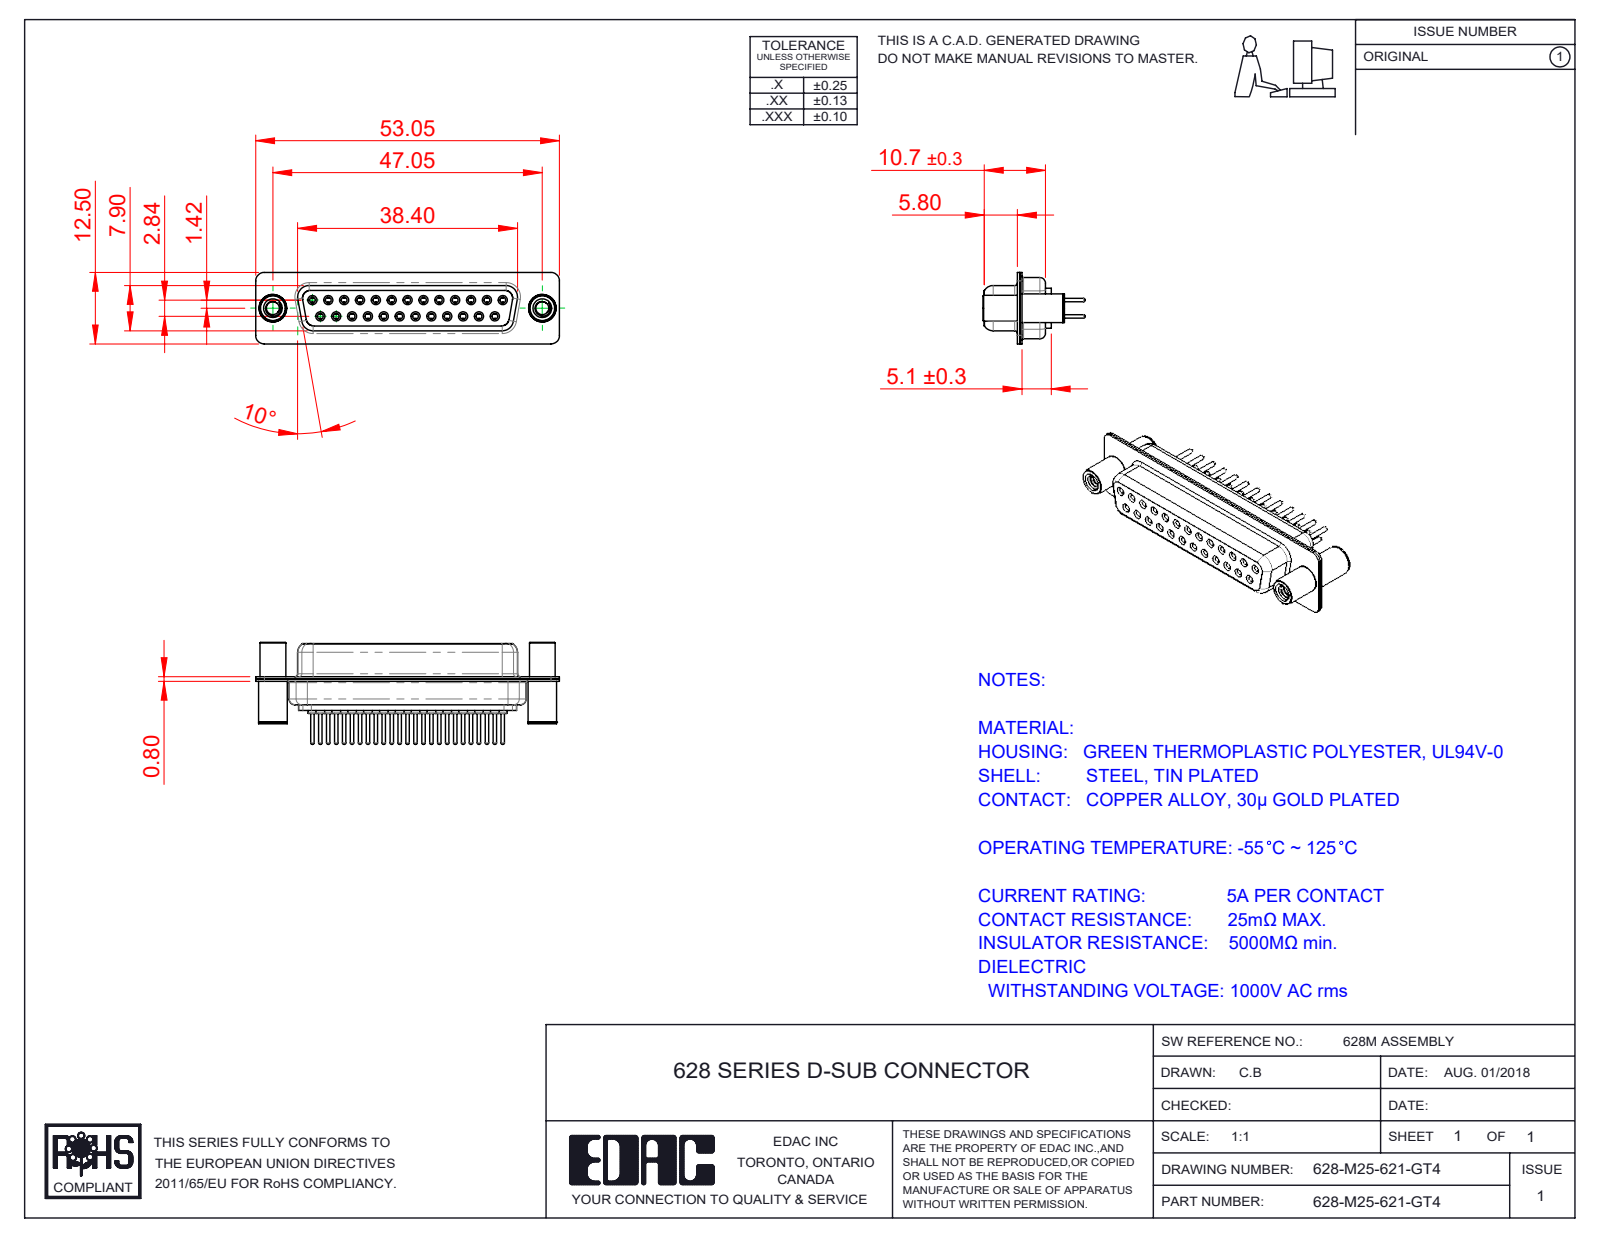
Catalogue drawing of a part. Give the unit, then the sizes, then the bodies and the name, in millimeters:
Units: millimetres
Overall size (bounding box): 53.05 × 17.8 × 12.5
Round holes (diameter × count): ⌀1 ×25, ⌀1.1 ×25, ⌀1.7 ×25, ⌀1.8 ×25, ⌀2 ×25, ⌀2.26 ×2, ⌀3.26 ×2, ⌀4 ×2, ⌀4.8 ×2
Round bosses / shafts (diameter × count): ⌀2.2 ×25, ⌀1.6 ×25, ⌀1.5 ×25, ⌀0.6 ×25, ⌀5 ×2, ⌀4.9 ×2, ⌀4.5 ×2
Partial cylindrical surfaces — rounded edges, fillets, slot ends (radius × count): R1.5 ×16, R2 ×12, R1.35 ×8, R1.6 ×8, R0.25 ×4, R0.5 ×4, R0.6 ×4, R0.65 ×4
Main face-to-face distances: 0.4, 1.4, 0.45, 8.45, 8.9, 1.8, 6.2, 7.05, 1, 1.85
Hole centre spacings: 3.16, 2.77, 5.54, 8.31, 11.08, 13.85, 5.04, 7.49
Volume: 4 027 mm³ · Surface area: 9 676 mm²
Bodies: 30 solids, 1740 faces (448 planar, 664 cylindrical, 628 other)
Part name (STEP PRODUCT): 628M Contact Row 2_21; 628M Shell Rear_25 Contacts; 628M Shell Front_25 Contacts; 628-M25-621-GT4 (+3 more)
STEP written by: SolidWorks 2020 (CONFIG_CONTROL_DESIGN)
